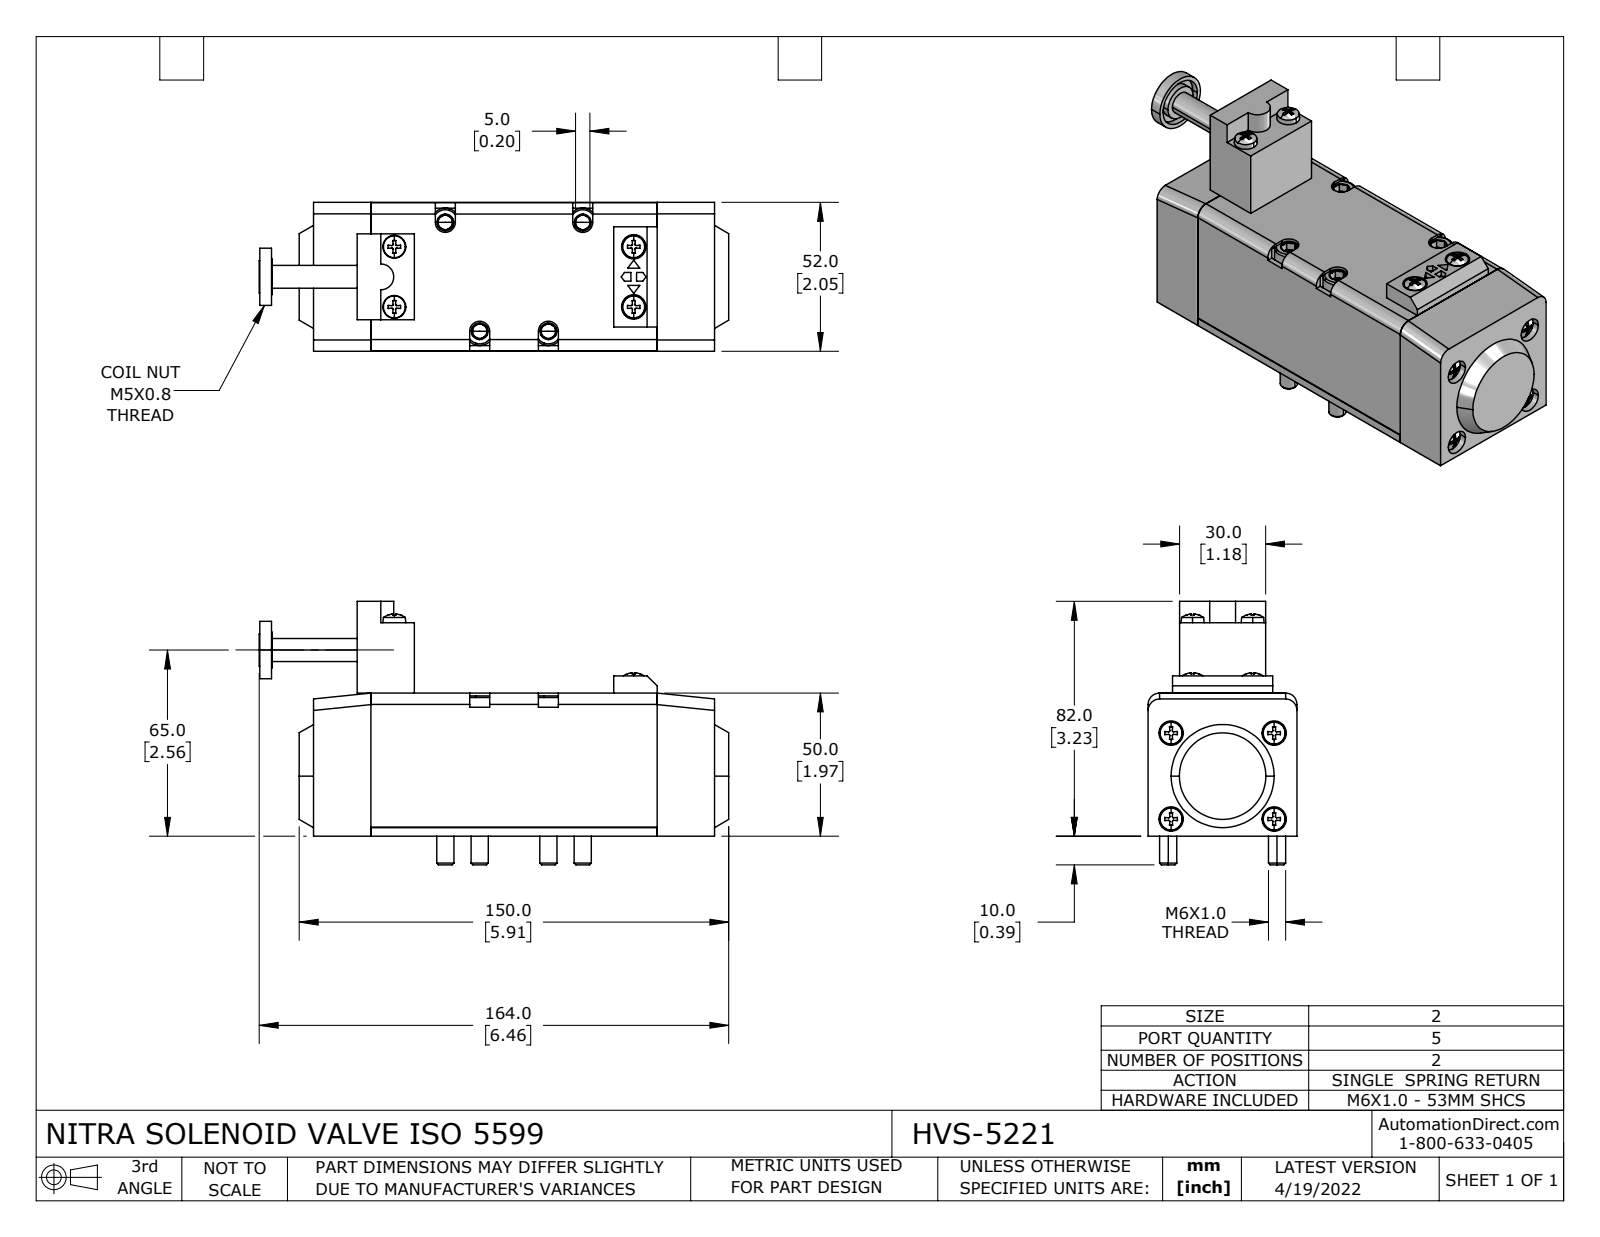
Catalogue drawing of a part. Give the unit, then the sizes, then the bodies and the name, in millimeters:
Units: millimetres
Overall size (bounding box): 164 × 92 × 52
Round holes (diameter × count): ⌀3.3 ×8, ⌀8.5 ×6, ⌀6.5 ×4, ⌀4.1 ×2, ⌀4.2 ×2, ⌀5 ×1, ⌀16.9 ×1
Round bosses / shafts (diameter × count): ⌀4 ×8, ⌀10 ×4, ⌀6 ×4, ⌀20 ×1, ⌀12.4 ×1, ⌀11.3 ×1, ⌀8 ×1
Partial cylindrical surfaces — rounded edges, fillets, slot ends (radius × count): R4 ×6, R3.5 ×4, R5 ×4, R4.5 ×1
Main face-to-face distances: 50, 100, 51.8, 51.9, 20, 120, 52, 15.2, 104.8, 5
Hole centre spacings: 19.7, 21, 30, 31, 34.1, 34.4, 36, 39.9
Volume: 389 000 mm³ · Surface area: 71 680 mm²
Bodies: 21 solids, 855 faces (448 planar, 147 cylindrical, 260 other)
Part name (STEP PRODUCT): HVS-5221
STEP written by: SolidWorks 2021 (CONFIG_CONTROL_DESIGN)
